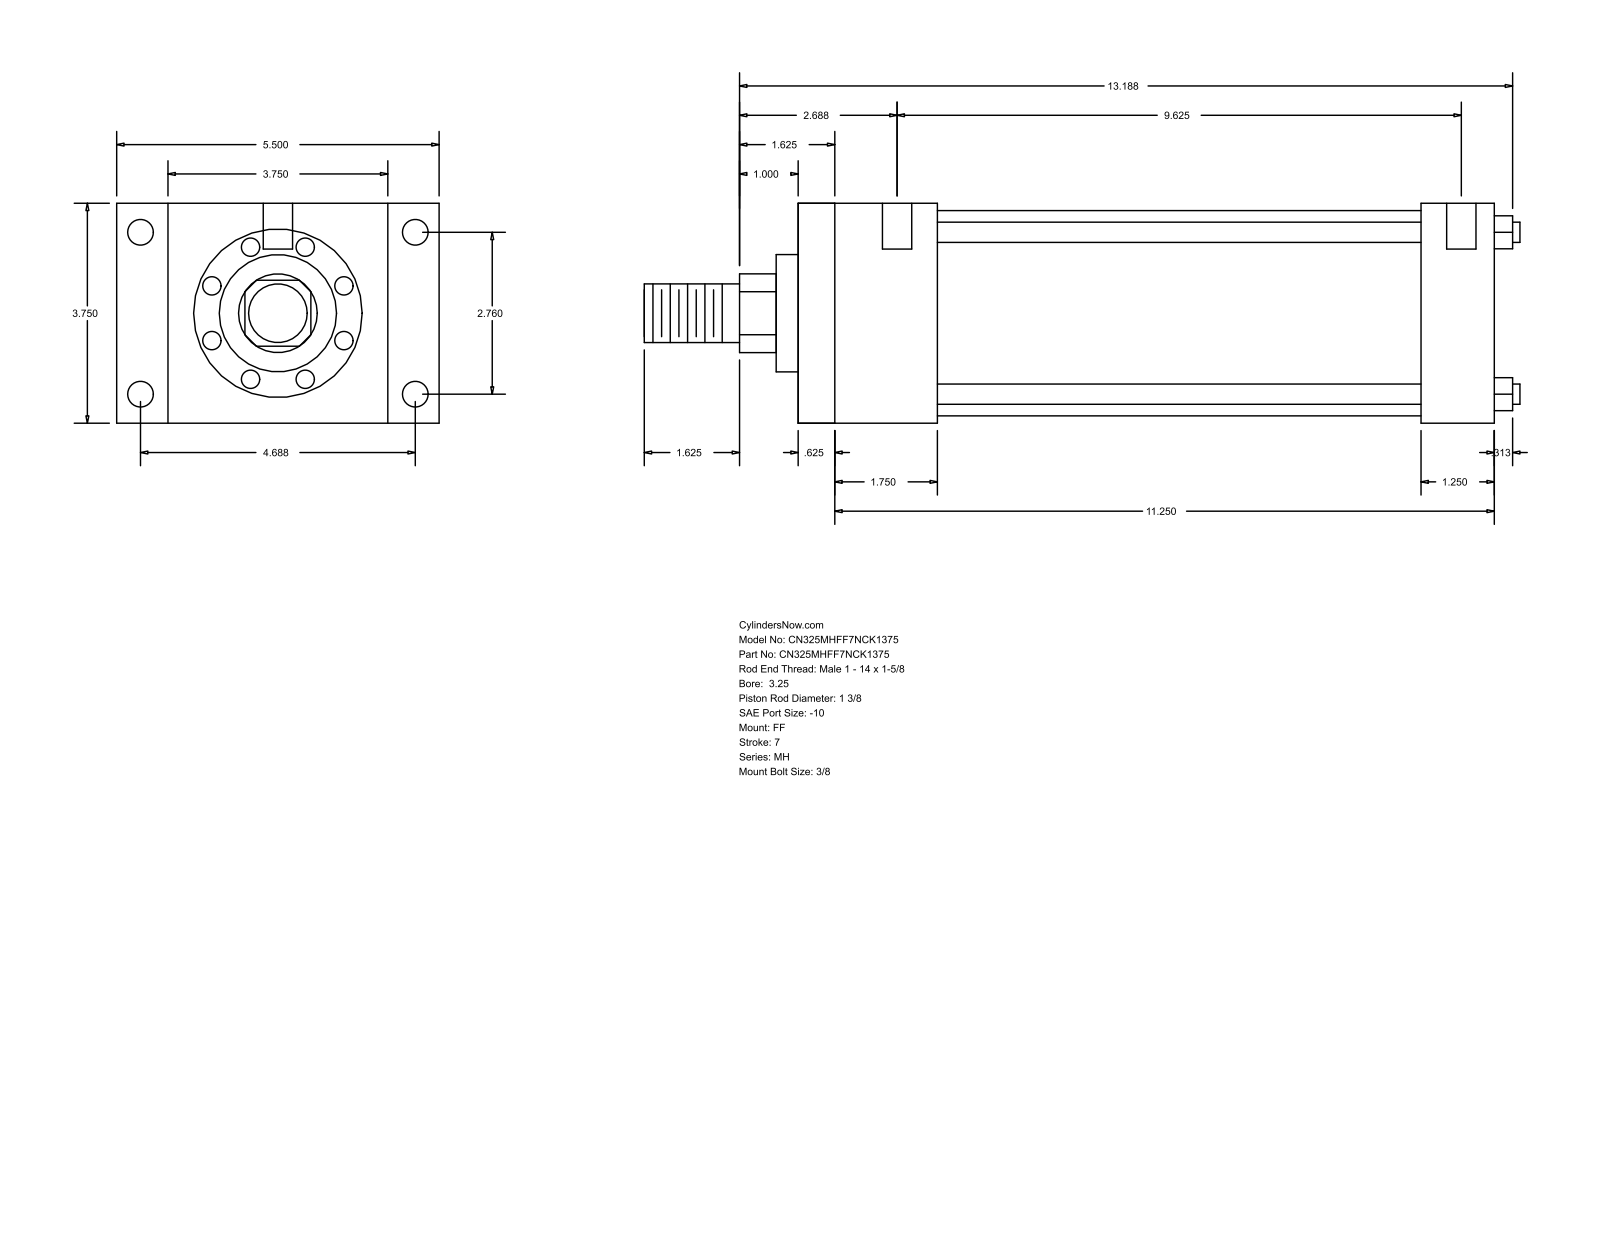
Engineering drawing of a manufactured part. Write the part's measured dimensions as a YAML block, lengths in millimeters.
part_name: "MH_FF__0325_1.375"
step_written_by: "GSSL Pune (CONFIG_CONTROL_DESIGN)"
units: millimeters
bodies: {solids: 0, faces: 92, planar: 64, cylindrical: 28, other: 0}
overall_size: [379.41, 139.7, 95.25]
round_holes:
  - {diameter: 5.56, count: 4}
  - {diameter: 11.13, count: 4}
  - {diameter: 12.7, count: 2}
round_bosses_or_shafts:
  - {diameter: 8.76, count: 4}
  - {diameter: 88.9, count: 1}
  - {diameter: 50.8, count: 1}
  - {diameter: 34.92, count: 1}
  - {diameter: 25.4, count: 1}
partial_cylinders:
  - {radius: 17.06, count: 1}
face_to_face_distances: [95.24, 301.62, 15.87, 285.75, 22.23, 117.47, 269.87, 254, 31.75, 60.32]
hole_center_spacings: [70.1, 119.06, 138.16, 250.83, 1.59, 4.76, 244.48, 246.07]
